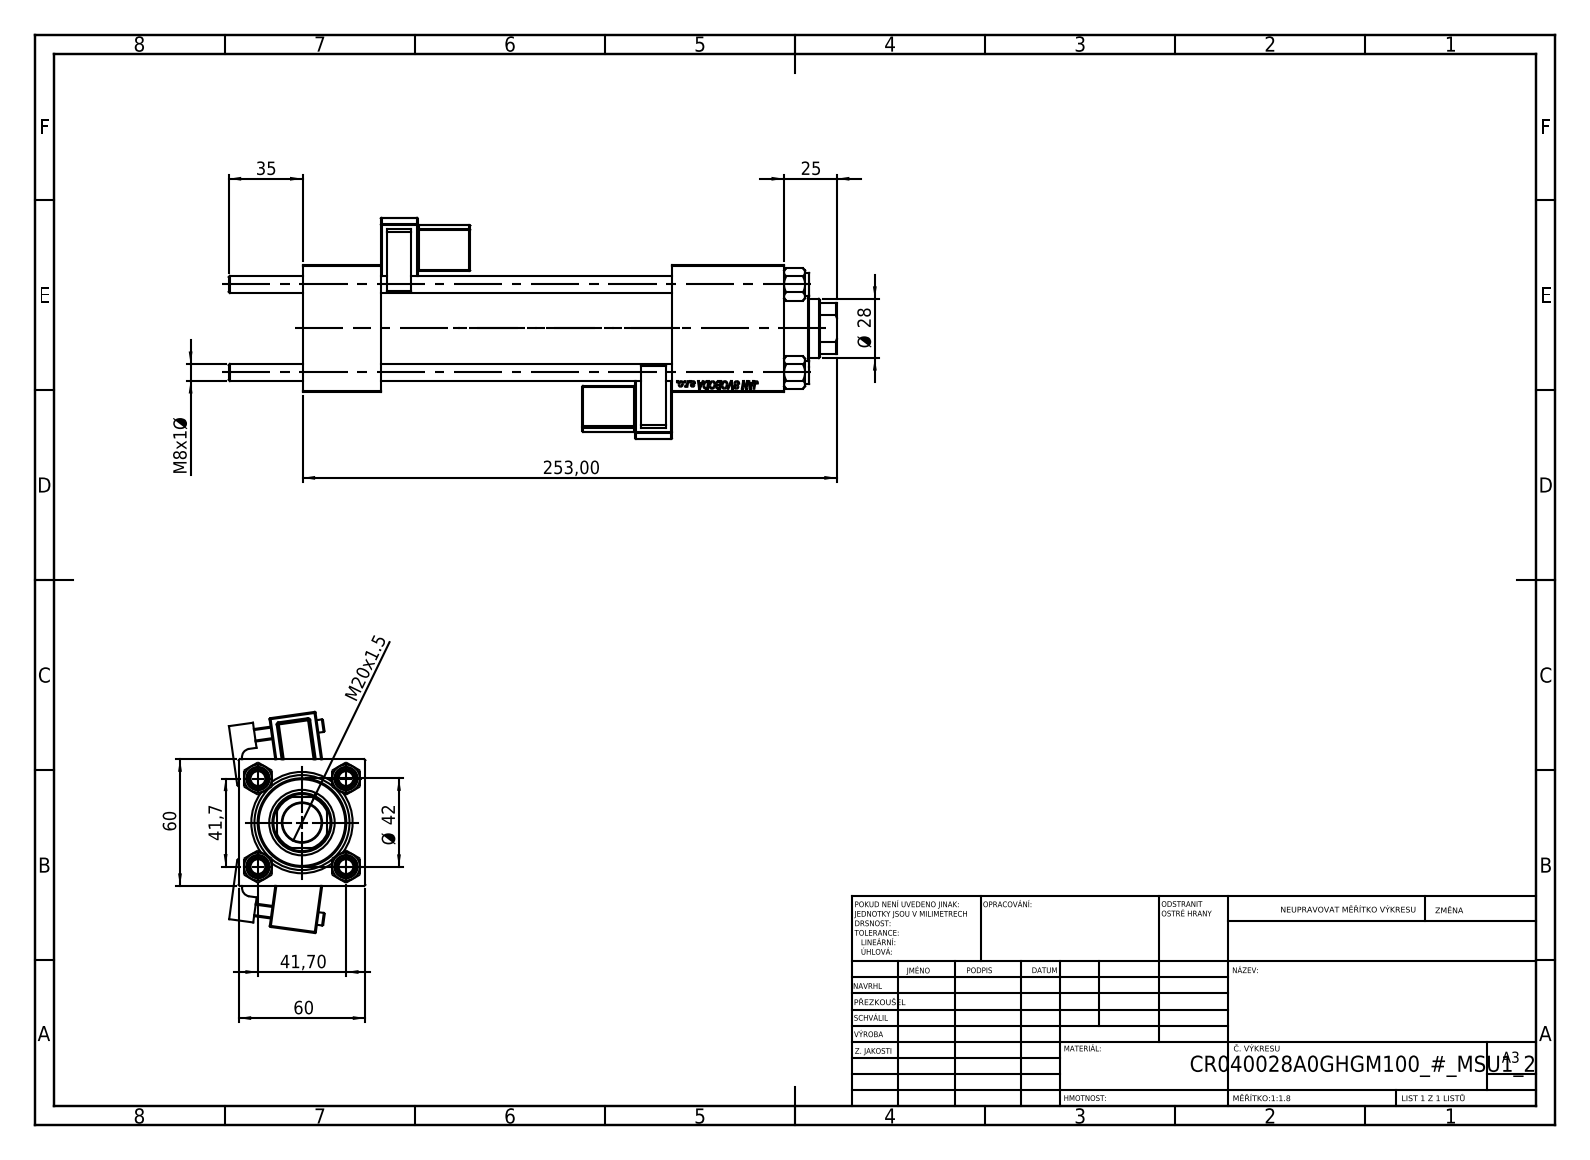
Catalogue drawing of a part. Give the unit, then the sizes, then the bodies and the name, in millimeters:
Units: millimetres
Overall size (bounding box): 288 × 104.69 × 64.58
Round holes (diameter × count): ⌀8 ×4, ⌀7 ×2, ⌀16.66 ×2, ⌀24 ×2, ⌀18.5 ×1, ⌀28 ×1, ⌀31 ×1, ⌀40 ×1, ⌀45 ×1
Round bosses / shafts (diameter × count): ⌀11 ×4, ⌀6 ×2, ⌀46 ×1, ⌀42 ×1
Partial cylindrical surfaces — rounded edges, fillets, slot ends (radius × count): R0.5 ×48, R1 ×2, R2.5 ×2, R4 ×2, R13.5 ×1
Main face-to-face distances: 60, 37, 175, 138, 53, 228, 191, 199.3, 162.3, 24.3
Hole centre spacings: 29.49, 41.7, 58.97, 172.5
Volume: 574 117 mm³ · Surface area: 168 889 mm²
Bodies: 13 solids, 1289 faces (579 planar, 138 cylindrical, 572 other)
Part name (STEP PRODUCT): V215CR_BODY_A; V215CR_VCP; V215_VC_A; CR025_012_A_0_G_A_G_M_020_+#_##_TYCINKA (+2 more)
STEP written by: SolidWorks 2019 (CONFIG_CONTROL_DESIGN)
